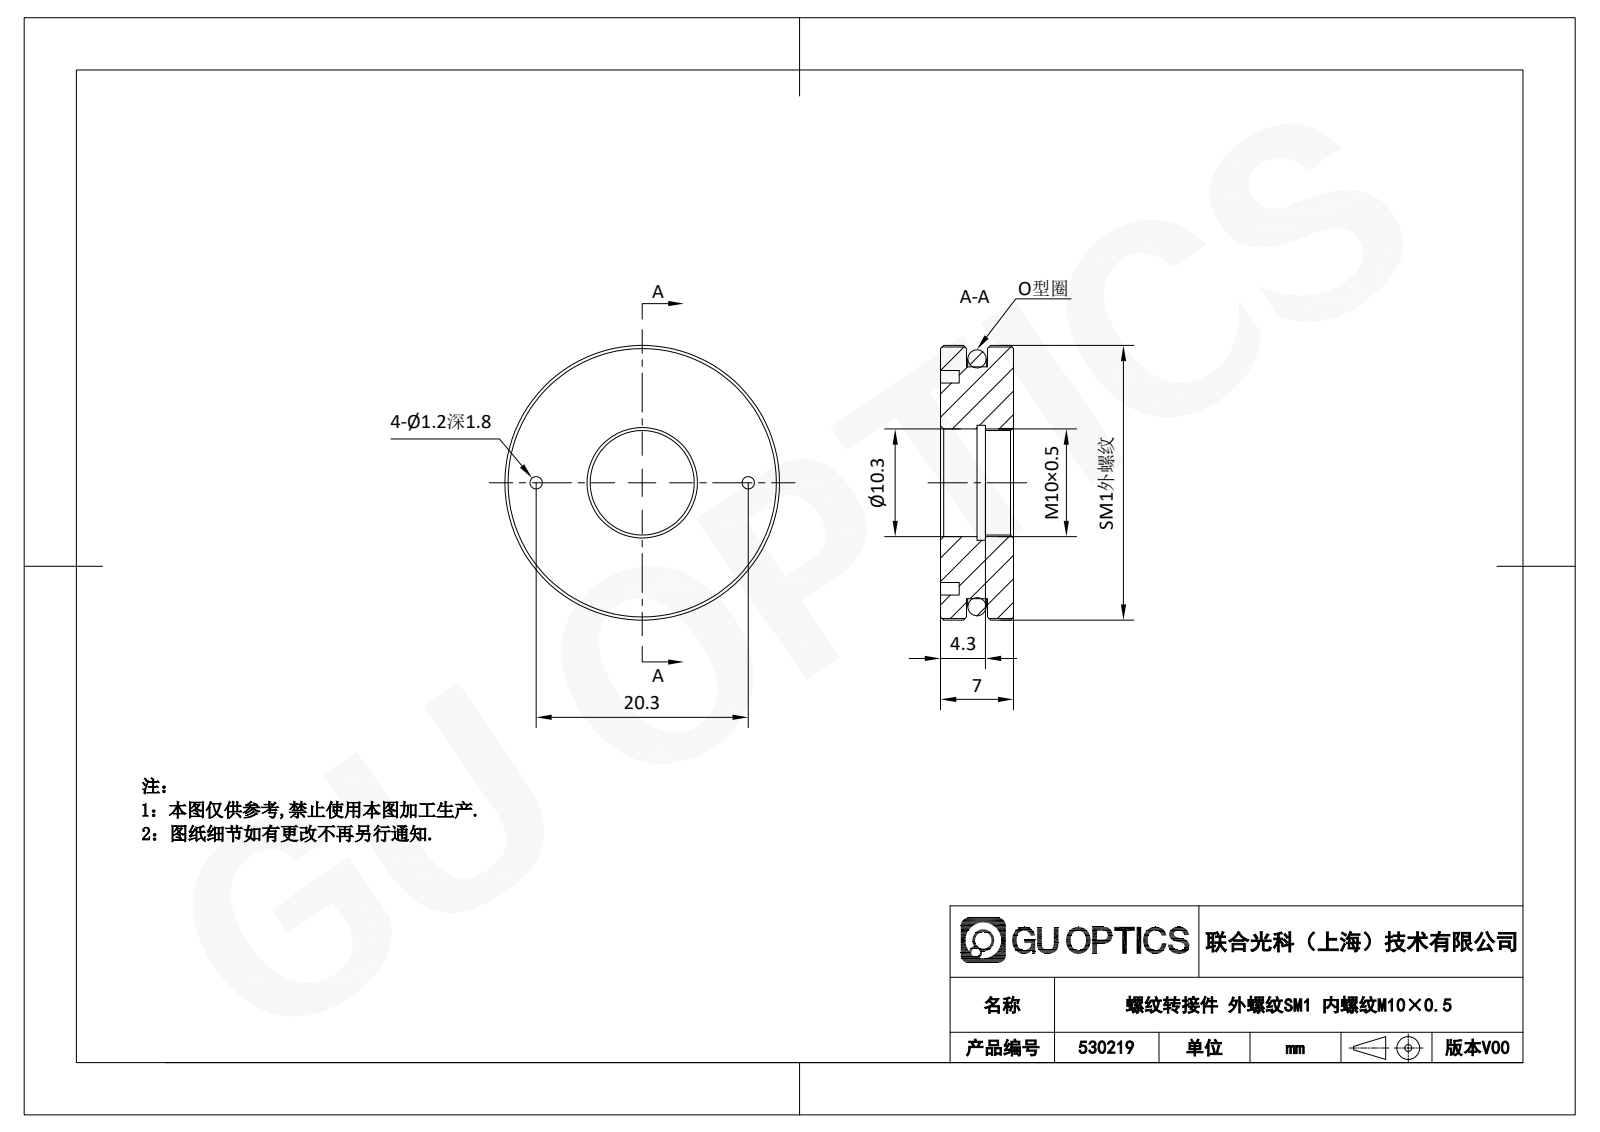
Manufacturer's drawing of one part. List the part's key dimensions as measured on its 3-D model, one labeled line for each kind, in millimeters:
Part name (STEP PRODUCT): 530219; O型圈
STEP written by: SolidWorks 2020 (CONFIG_CONTROL_DESIGN)
Units: millimetres
Bodies: 2 solids, 27 faces (10 planar, 10 cylindrical, 7 other)
Overall size (bounding box): 26.29 × 26.29 × 7
Volume: 3 066 mm³ · Surface area: 2 418 mm²
Round holes (diameter × count): ⌀1.2 ×4, ⌀10 ×1, ⌀10.3 ×1, ⌀11 ×1
Round bosses / shafts (diameter × count): ⌀26.29 ×1, ⌀22.2 ×1
Main face-to-face distances: 7, 2.5, 4.5, 2, 3.5, 1, 1.8, 2.7, 4.3, 0.8
Hole centre spacings: 10.15, 14.35, 20.3
